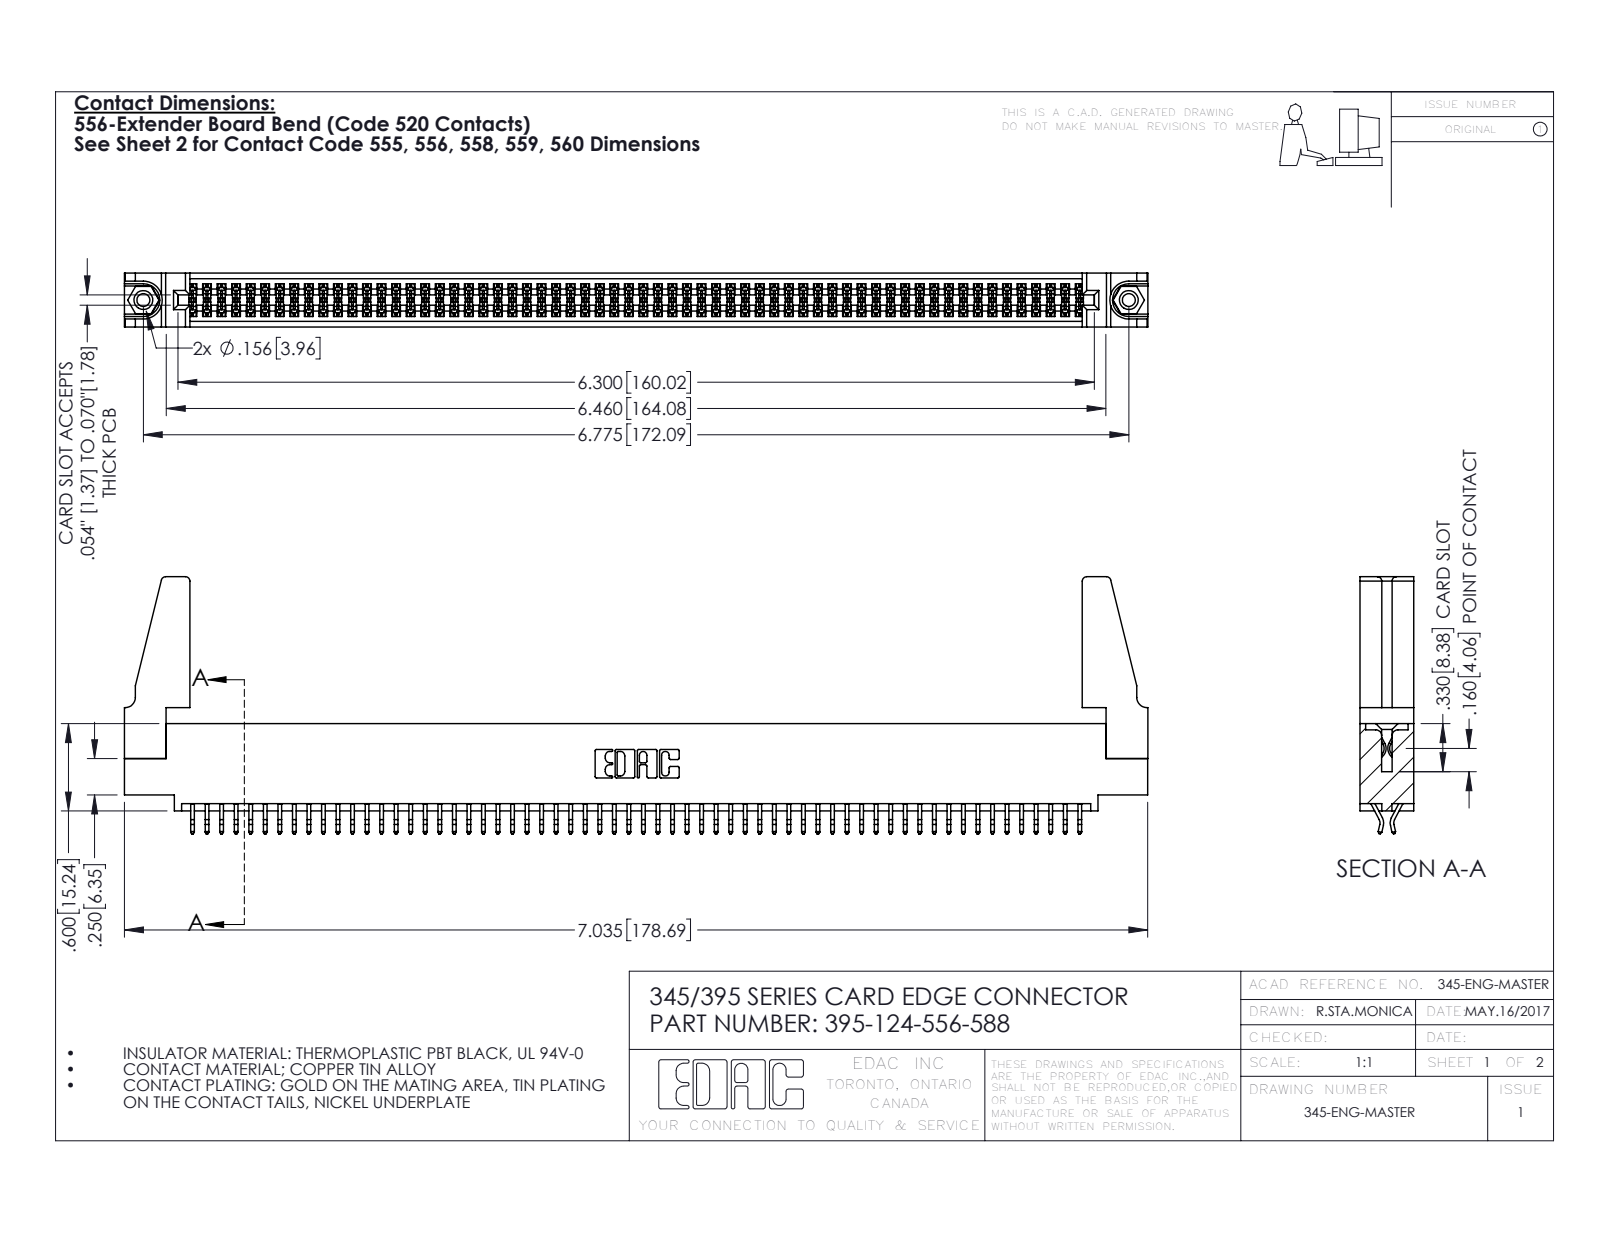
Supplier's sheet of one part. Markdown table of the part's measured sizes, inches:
| quantity | value |
| --- | --- |
| part name | 395-124-556-588; 345-250-001_345-250-001-102; 345-220-078_345-220-088; 345 Part_0.110 Offset - 0.156 Dia-TH (+1 more) |
| STEP written by | SolidWorks 2016 (CONFIG_CONTROL_DESIGN) |
| units | inches |
| bodies | 129 solids, 7198 faces (4744 planar, 2438 cylindrical, 16 other) |
| overall size | 7.036 × 1.767 × 0.37 |
| volume | 1.264 in³ |
| surface area | 45.44 in² |
| round holes (diameter × count) | 0.089 × 2, 0.125 × 2, 0.156 × 2, 0.064 × 1 |
| round bosses / shafts (diameter × count) | 0.155 × 2 |
| partial cylindrical surfaces (radius × count) | 0.006 × 186, 0.01 × 22, 0.03 × 8, 0.007 × 6, 0.031 × 6, 0.026 × 3, 0.01 × 2, 0.014 × 2 |
| main face-to-face distances | 0.072, 0.298, 0.37, 0.025, 0.2, 0.098, 0.272, 0.225, 0.175, 0.149 |
| hole center spacings | 0.27, 6.539, 6.775 |
